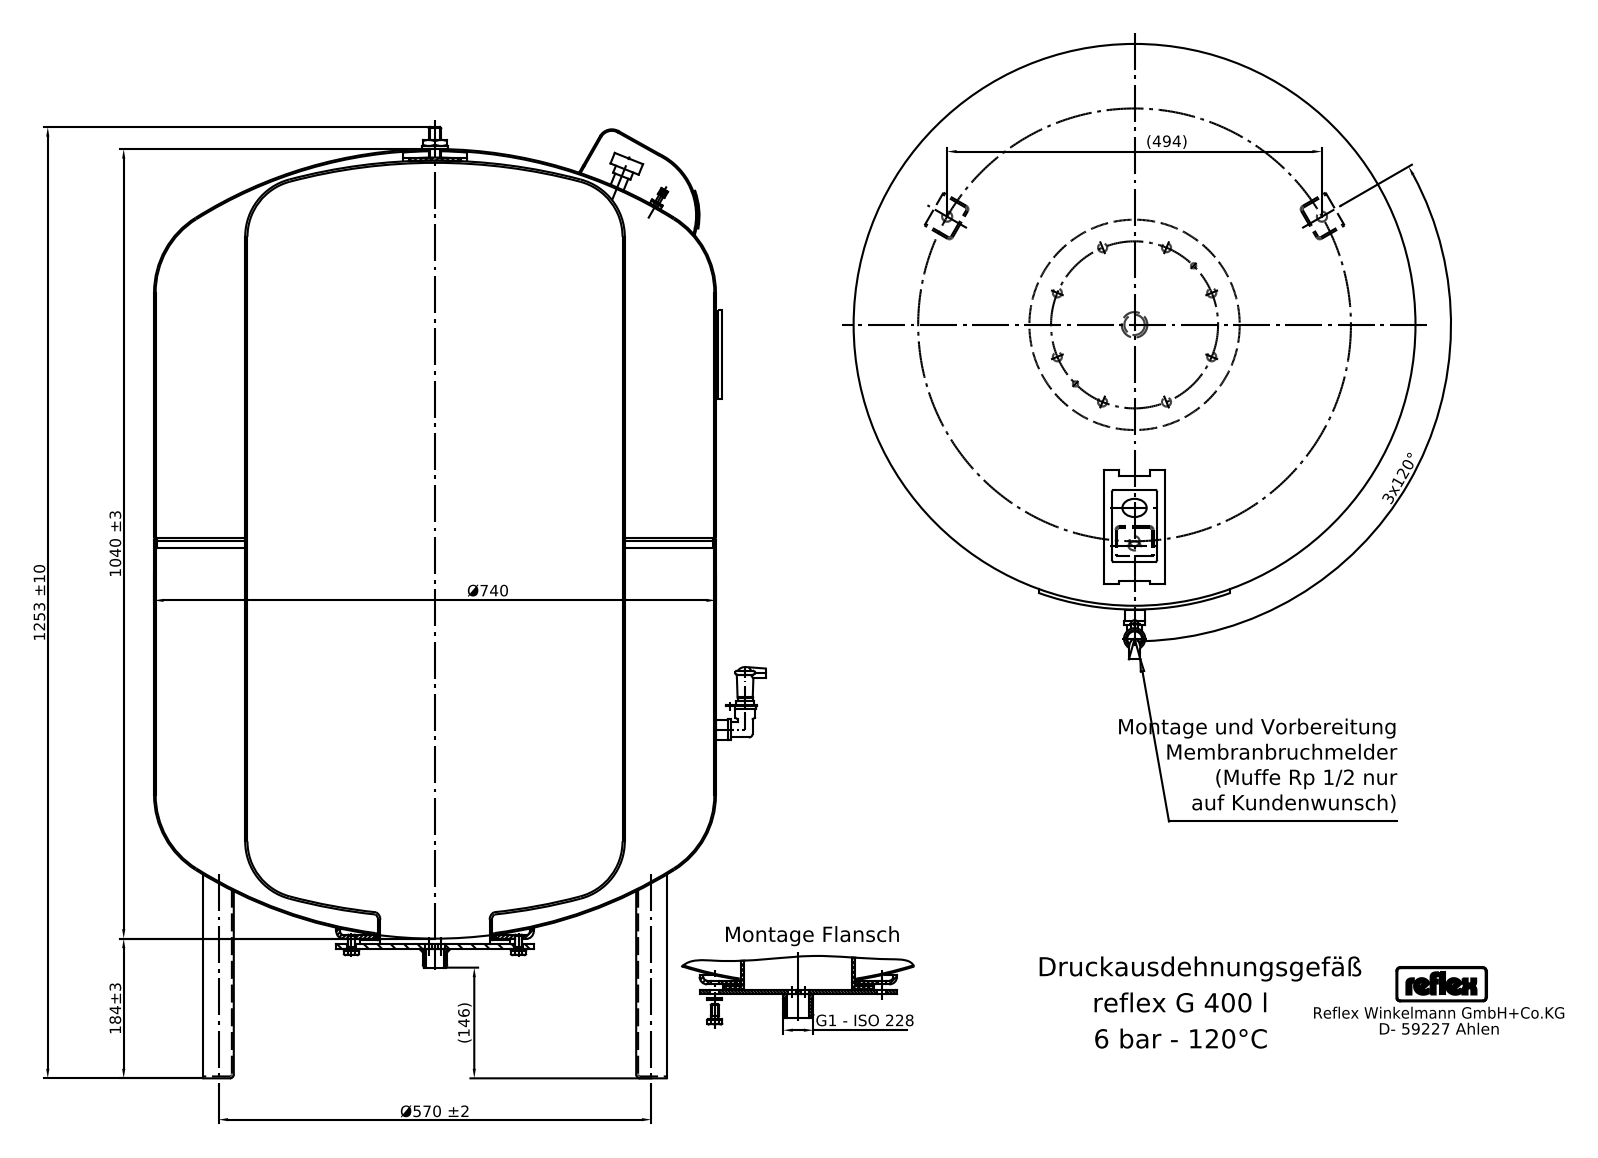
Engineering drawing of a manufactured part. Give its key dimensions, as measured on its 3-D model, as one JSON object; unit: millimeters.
{"step_written_by": "Mechanical Desktop 2008 (CONFIG_CONTROL_DESIGN)", "units": "millimeters", "bodies": {"solids": 21, "faces": 505, "planar": 229, "cylindrical": 183, "other": 93}, "overall_size": [1253, 805, 741.14], "volume_mm3": 392400000, "surface_area_mm2": 4946000, "round_holes": [[13.4, 3], [2.48, 1], [7, 1], [8, 1], [10, 1], [11.4, 1], [161, 1], [250, 1]], "round_bosses_or_shafts": [[10, 9], [28, 2], [26, 2], [20, 2], [740, 1], [260, 1], [230, 1], [62, 1]], "partial_cylinders_radius": [[1, 15], [2.5, 15], [5, 15], [3.94, 4], [1.57, 3], [2.69, 2], [4.72, 2], [6.49, 2]], "face_to_face_distances": [662, 2.5, 47.5, 196, 858, 6, 202, 864, 45, 50], "hole_center_spacings": [285, 493.64, 346.37, 385.5, 670.5]}
